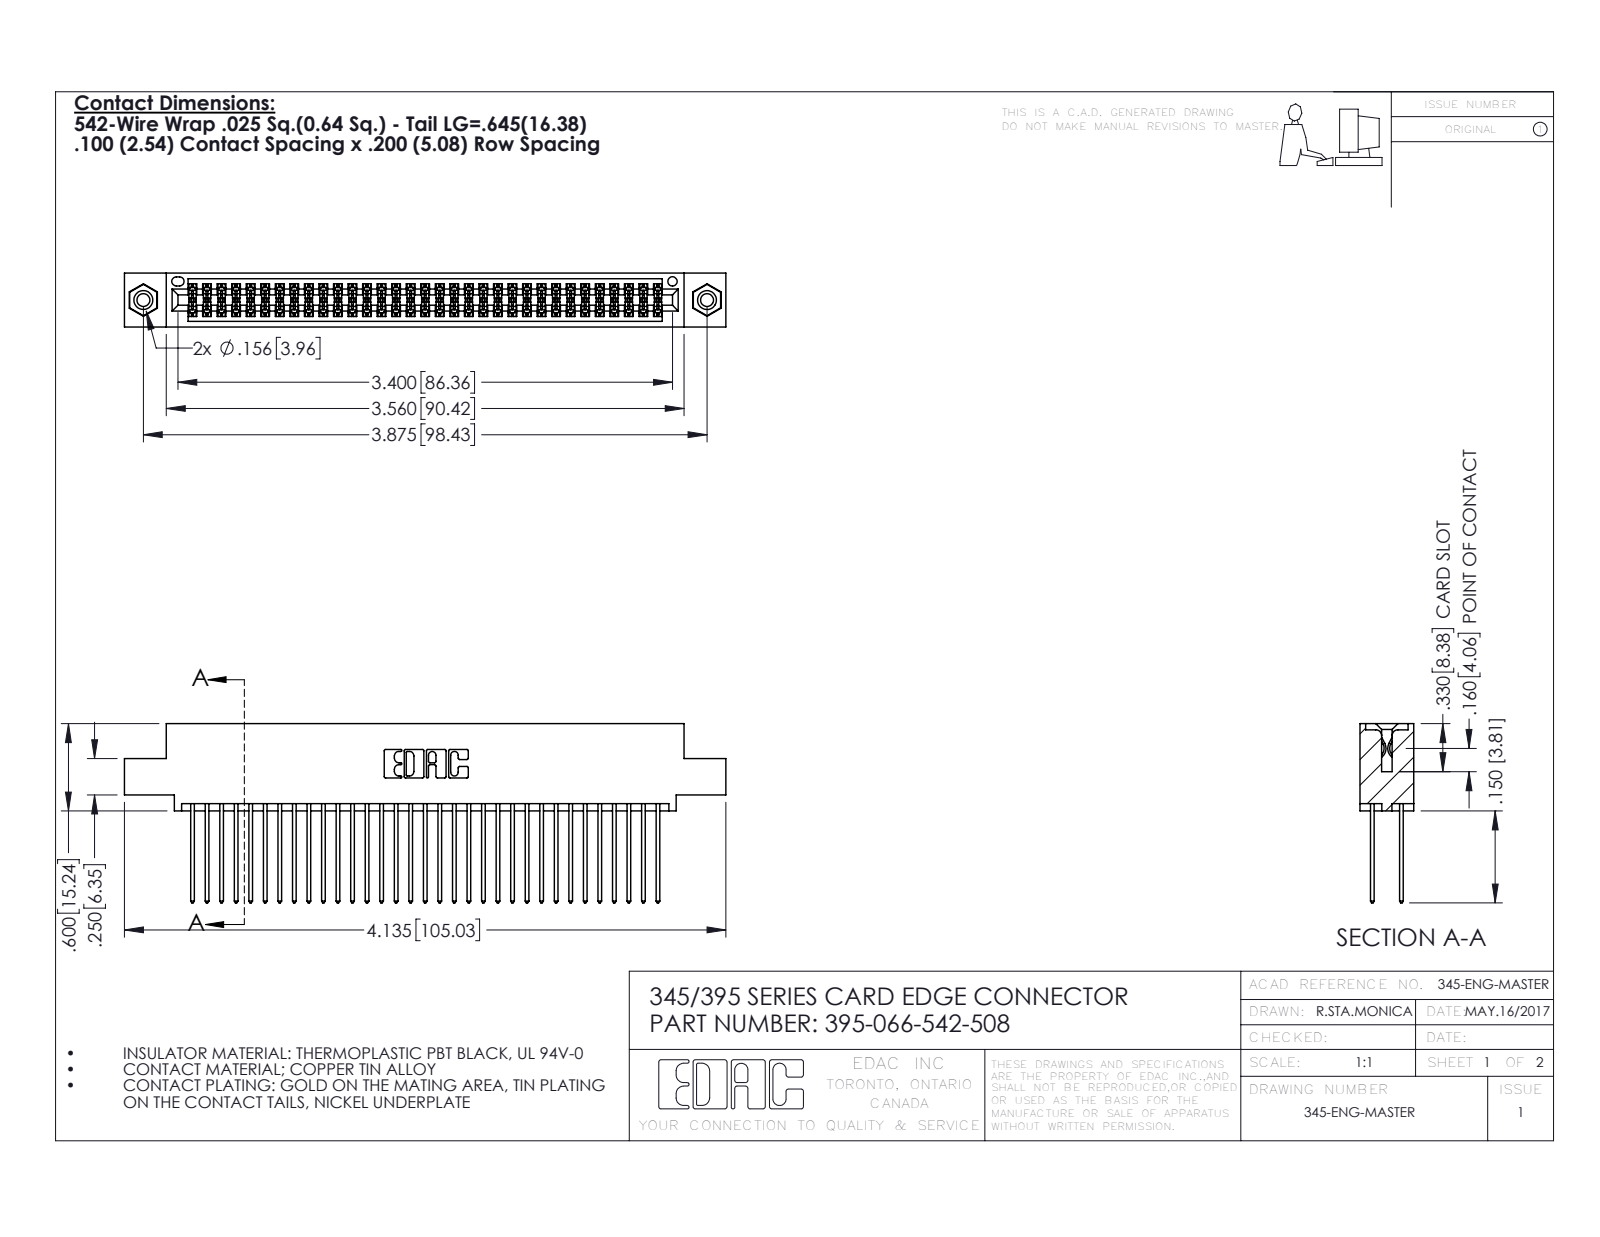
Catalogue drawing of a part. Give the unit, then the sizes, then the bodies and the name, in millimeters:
Units: millimetres
Overall size (bounding box): 105 × 31.3 × 9.4
Round holes (diameter × count): ⌀2.3 ×2, ⌀3.2 ×2, ⌀4 ×2, ⌀1.6 ×1
Round bosses / shafts (diameter × count): ⌀3.9 ×2
Partial cylindrical surfaces — rounded edges, fillets, slot ends (radius × count): R0.2 ×99, R0.3 ×66, R0.3 ×22, R0.2 ×6, R0.8 ×6, R0.7 ×3, R0.4 ×2, R0.5 ×2
Main face-to-face distances: 1.8, 7.6, 5.1, 2.5, 6.9, 0.6, 9.4, 5.7, 4.4, 3.8
Hole centre spacings: 6.9, 92.5, 98.4
Volume: 10 300 mm³ · Surface area: 16 660 mm²
Bodies: 69 solids, 3490 faces (2294 planar, 1180 cylindrical, 16 other)
Part name (STEP PRODUCT): 345-292-001_345-293-142; 395-066-542-508; 345-250-001_345-250-003-102; 345 Part_0.110 Offset - 0.156 Dia-TI
STEP written by: SolidWorks 2016 (CONFIG_CONTROL_DESIGN)
